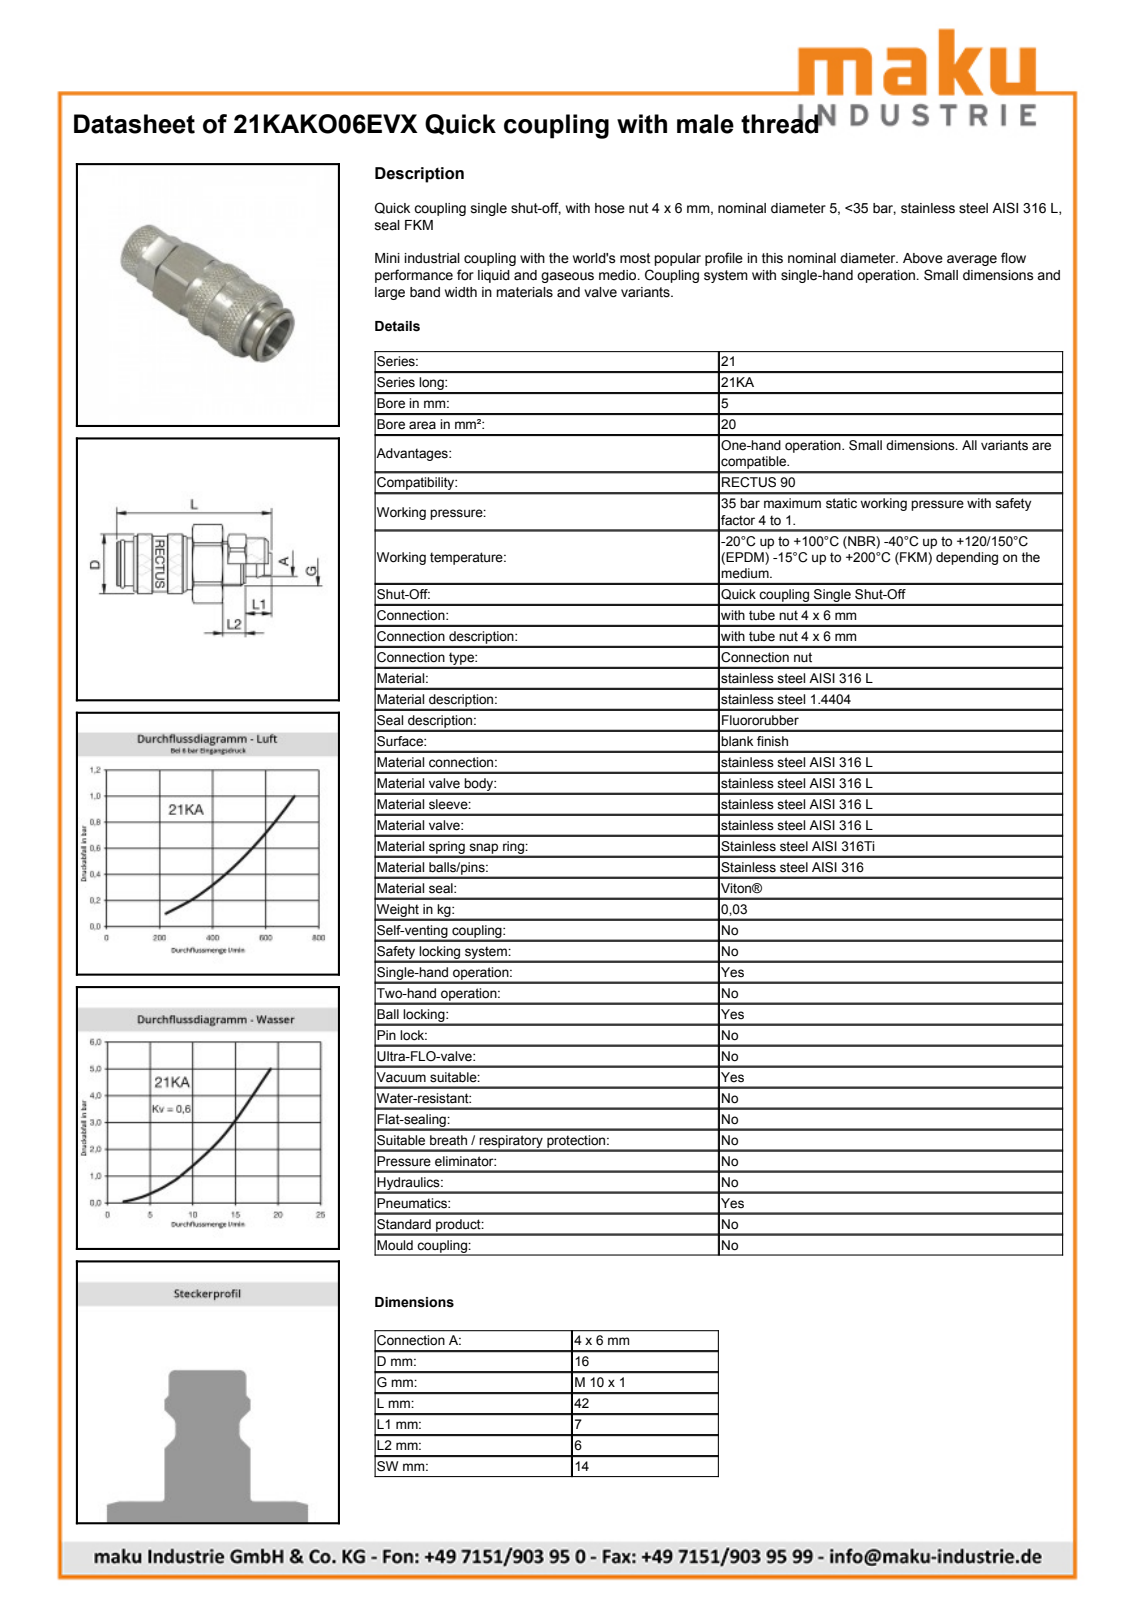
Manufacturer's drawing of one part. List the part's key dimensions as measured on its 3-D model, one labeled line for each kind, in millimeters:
Part name (STEP PRODUCT): D107099
STEP written by: Autodesk Inventor 2013 (AUTOMOTIVE_DESIGN)
Units: millimetres
Bodies: 2 solids, 493 faces (159 planar, 73 cylindrical, 261 other)
Overall size (bounding box): 42 × 16.15 × 16.15
Volume: 5 760 mm³ · Surface area: 4 036 mm²
Round holes (diameter × count): ⌀6.2 ×1, ⌀9.45 ×1, ⌀12.15 ×1, ⌀14 ×1
Round bosses / shafts (diameter × count): ⌀16.15 ×1, ⌀15.1 ×1, ⌀12 ×1, ⌀11.4 ×1, ⌀11.15 ×1, ⌀10 ×1, ⌀8.6 ×1, ⌀4.6 ×1
Partial cylindrical surfaces — rounded edges, fillets, slot ends (radius × count): R5.37 ×1, R6.75 ×1, R7.45 ×1, R7.9 ×1
Main face-to-face distances: 14, 12, 28.9, 39.9, 11, 4.6, 24.3, 35.3, 11.9, 7.3
